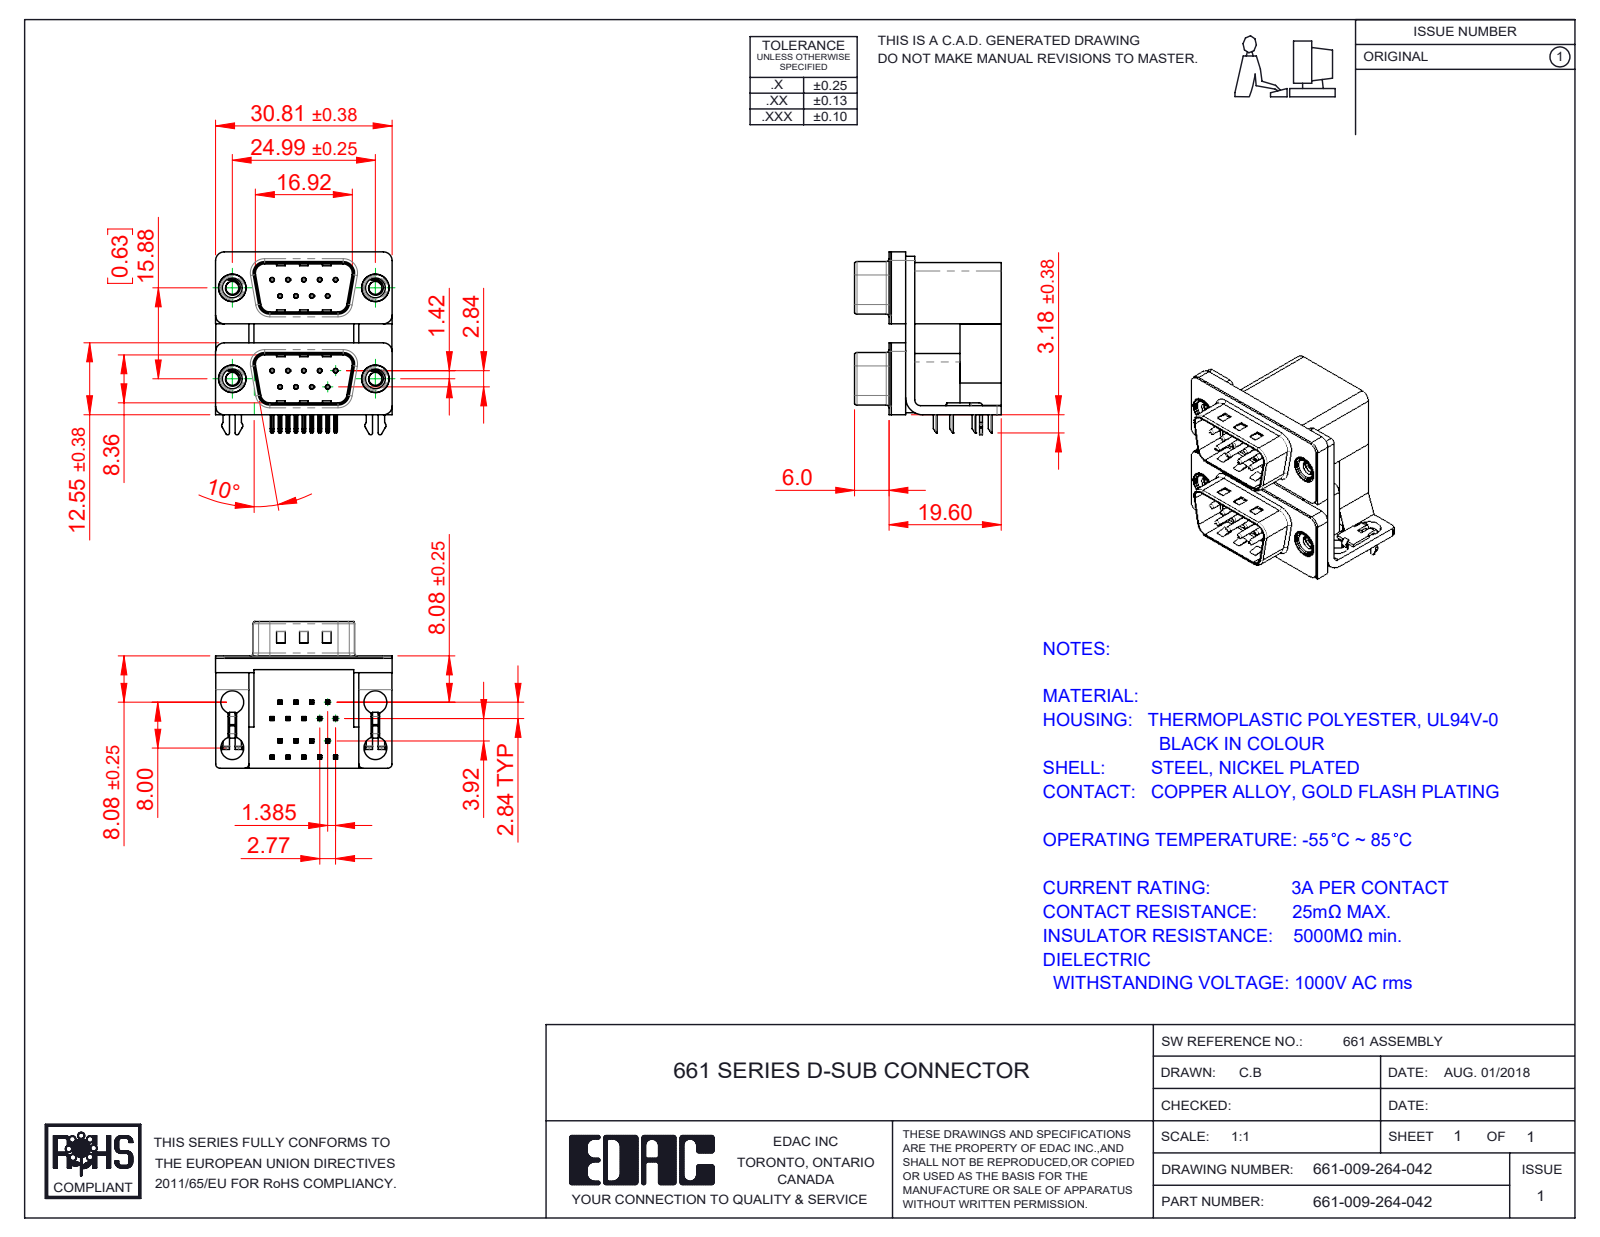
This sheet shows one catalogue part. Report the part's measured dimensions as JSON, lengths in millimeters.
{"part_name": "661 Contact Bottom Lower; 661-009-264-042; 661 Housing Spacer_09 Contacts L; 661 Threaded Rivet_4-40 (+8 more)", "step_written_by": "SolidWorks 2020 (CONFIG_CONTROL_DESIGN)", "units": "millimeters", "bodies": {"solids": 31, "faces": 2056, "planar": 1230, "cylindrical": 624, "other": 202}, "overall_size": [31.93, 30.81, 25.6], "volume_mm3": 9830, "surface_area_mm2": 11562, "round_holes": [[0.35, 18], [0.8, 18], [4, 8], [2.26, 4], [3.5, 4], [4.8, 4], [5, 4]], "round_bosses_or_shafts": [[0.75, 18], [4.9, 4], [4.75, 4], [3.9, 4]], "partial_cylinders_radius": [[0.25, 78], [0.12, 36], [0.5, 20], [1.5, 13], [0.75, 10], [0.9, 8], [1.6, 8], [2, 8]], "face_to_face_distances": [0.4, 2.5, 16.7, 19.2, 15.87, 7.2, 9.5, 12, 1.6, 19.6], "hole_center_spacings": [3.16, 16.12, 2.77, 15.88, 16.82, 18.77, 5.54, 5.04]}
